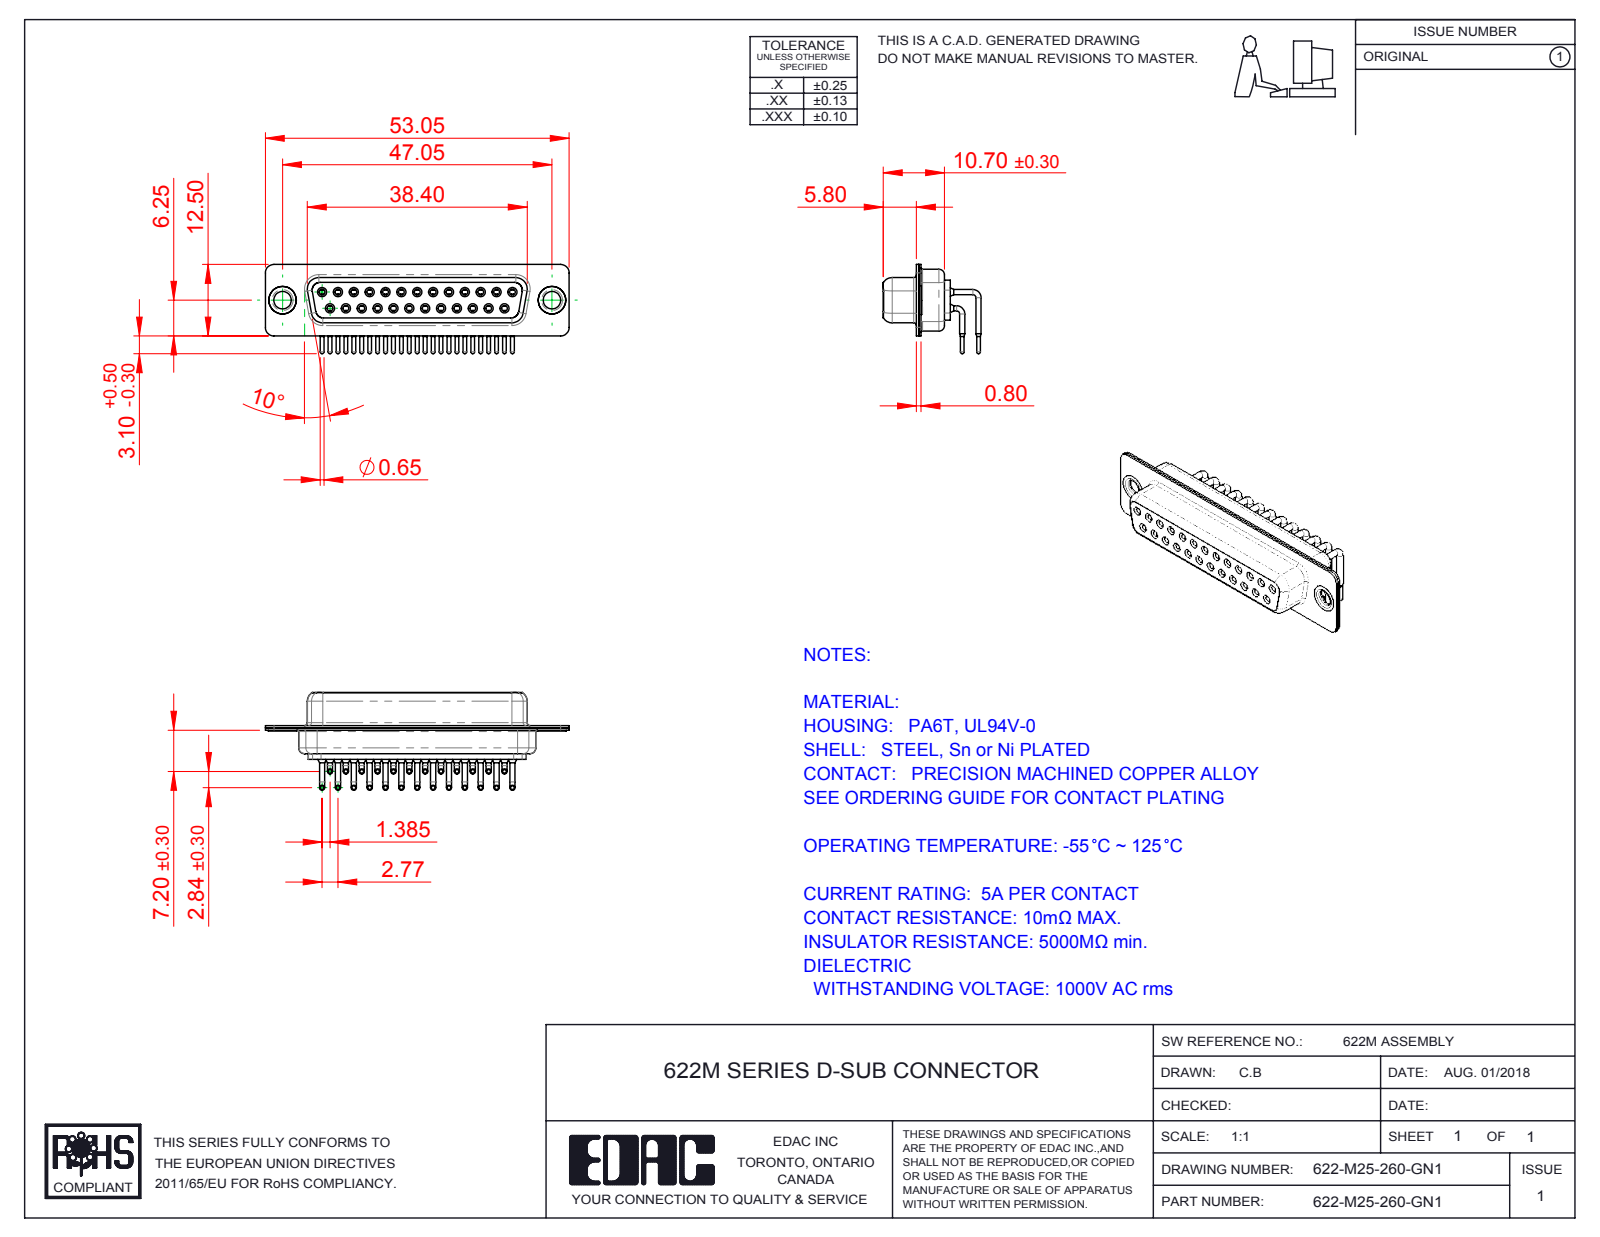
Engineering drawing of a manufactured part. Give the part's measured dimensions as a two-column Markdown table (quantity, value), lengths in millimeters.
| quantity | value |
| --- | --- |
| part name | 622M Contact Row 2; 622M Contact Row 1; 622M Thru Hole Rivet; 622M Housing_25 Contacts (+3 more) |
| STEP written by | SolidWorks 2016 (CONFIG_CONTROL_DESIGN) |
| units | millimeters |
| bodies | 30 solids, 1578 faces (442 planar, 696 cylindrical, 440 other) |
| overall size | 53.05 × 17.09 × 15.6 |
| volume | 3 773 mm³ |
| surface area | 9 352 mm² |
| round holes (diameter × count) | 1 × 25, 1.1 × 25, 1.7 × 25, 1.8 × 25, 2 × 25, 3.05 × 2, 4 × 2, 4.8 × 2 |
| round bosses / shafts (diameter × count) | 0.9 × 50, 1.6 × 25, 1.5 × 25, 0.65 × 25, 5 × 2, 4.9 × 2, 3.55 × 2 |
| partial cylindrical surfaces (radius × count) | 1.5 × 16, 2 × 12, 1.35 × 8, 1.6 × 8, 0.25 × 4, 0.5 × 4, 0.6 × 4, 0.65 × 4 |
| main face-to-face distances | 0.4, 1.45, 8.95, 6.2, 1.9, 8.5, 0.45, 7.05, 2.3, 0.85 |
| hole center spacings | 3.16, 2.77, 5.54, 8.31, 11.08, 13.85, 16.62, 5.03 |
